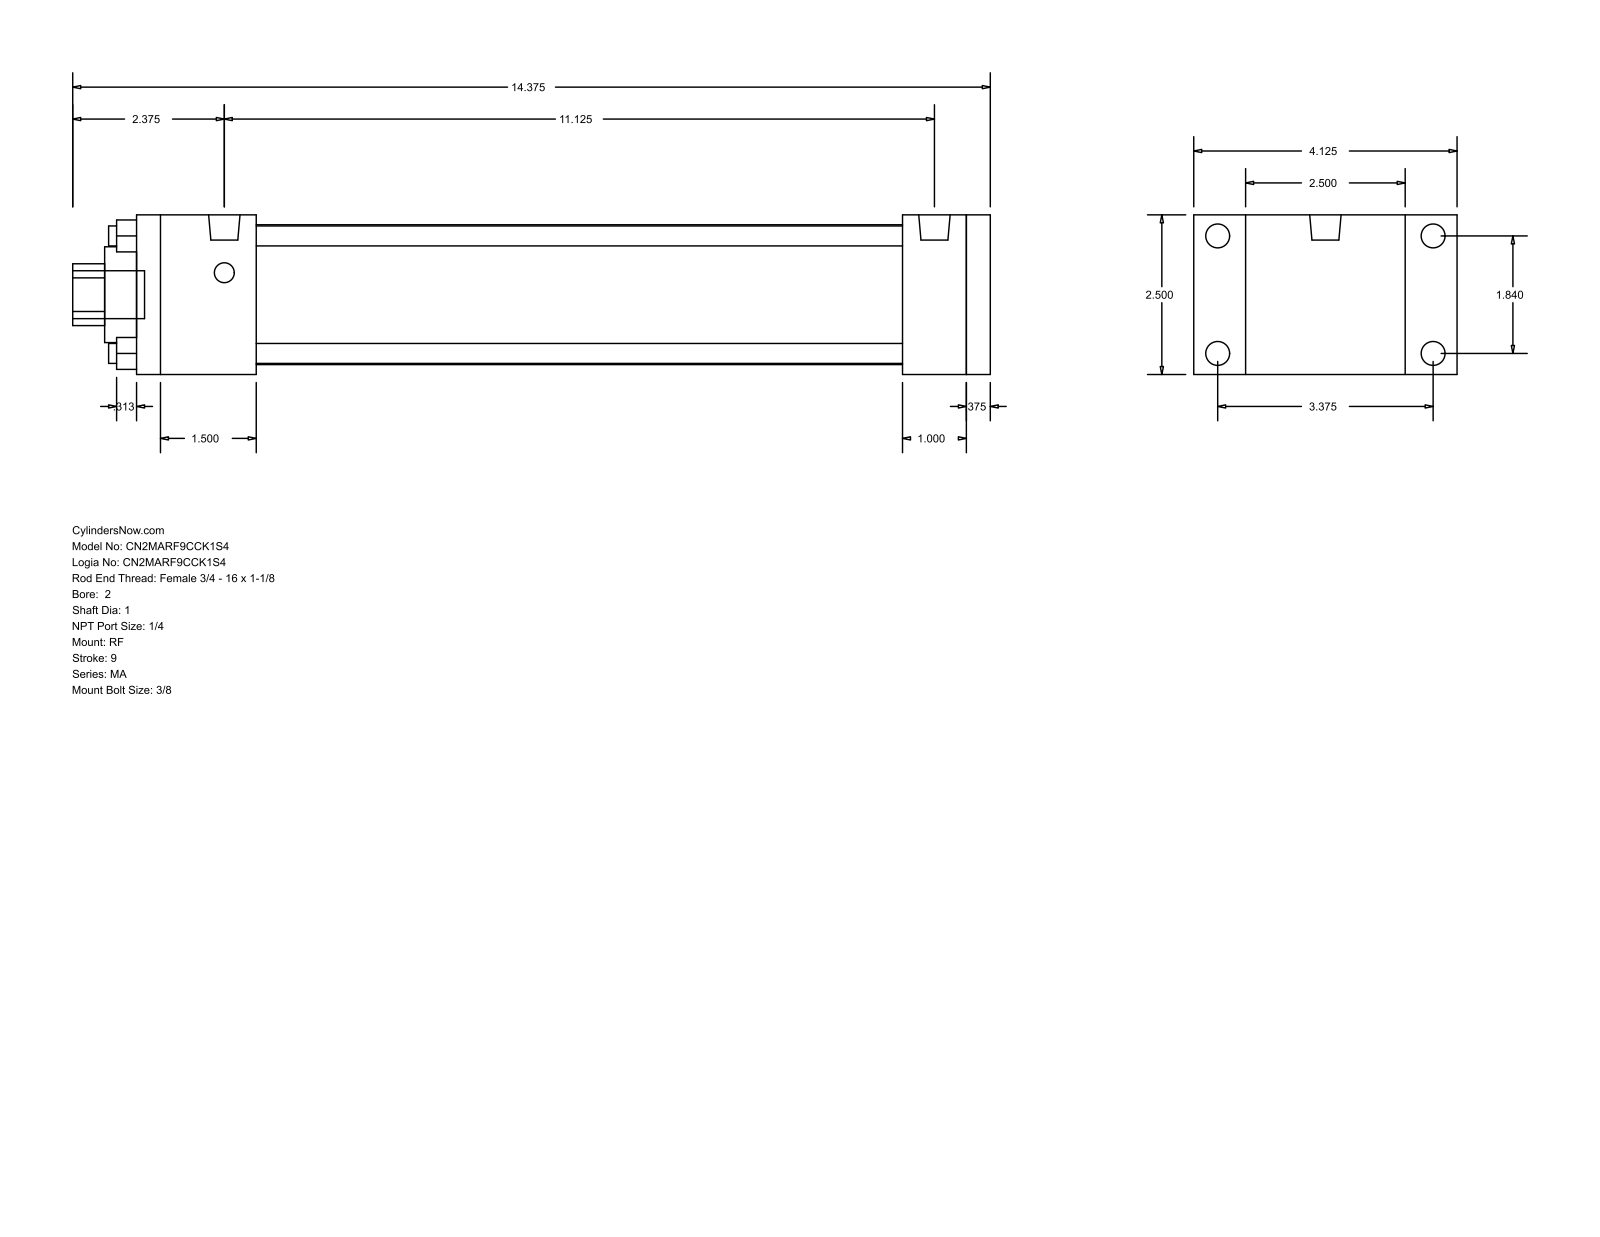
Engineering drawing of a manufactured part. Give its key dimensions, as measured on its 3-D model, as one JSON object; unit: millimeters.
{"part_name": "MA_RF__0200_1", "step_written_by": "GSSL Pune (CONFIG_CONTROL_DESIGN)", "units": "millimeters", "bodies": {"solids": 0, "faces": 92, "planar": 64, "cylindrical": 28, "other": 0}, "overall_size": [365.12, 104.78, 63.5], "round_holes": [[7.94, 4], [25.4, 1], [38.1, 1], [55.63, 1]], "round_bosses_or_shafts": [[9.53, 4], [7.94, 4], [12.49, 2], [19.05, 1]], "partial_cylinders_radius": [[12.29, 1]], "face_to_face_distances": [63.5, 330.2, 9.52, 339.72, 25.4, 20.64, 12.7, 47.63, 282.57, 292.09], "hole_center_spacings": [33.05, 46.74, 66.1]}
